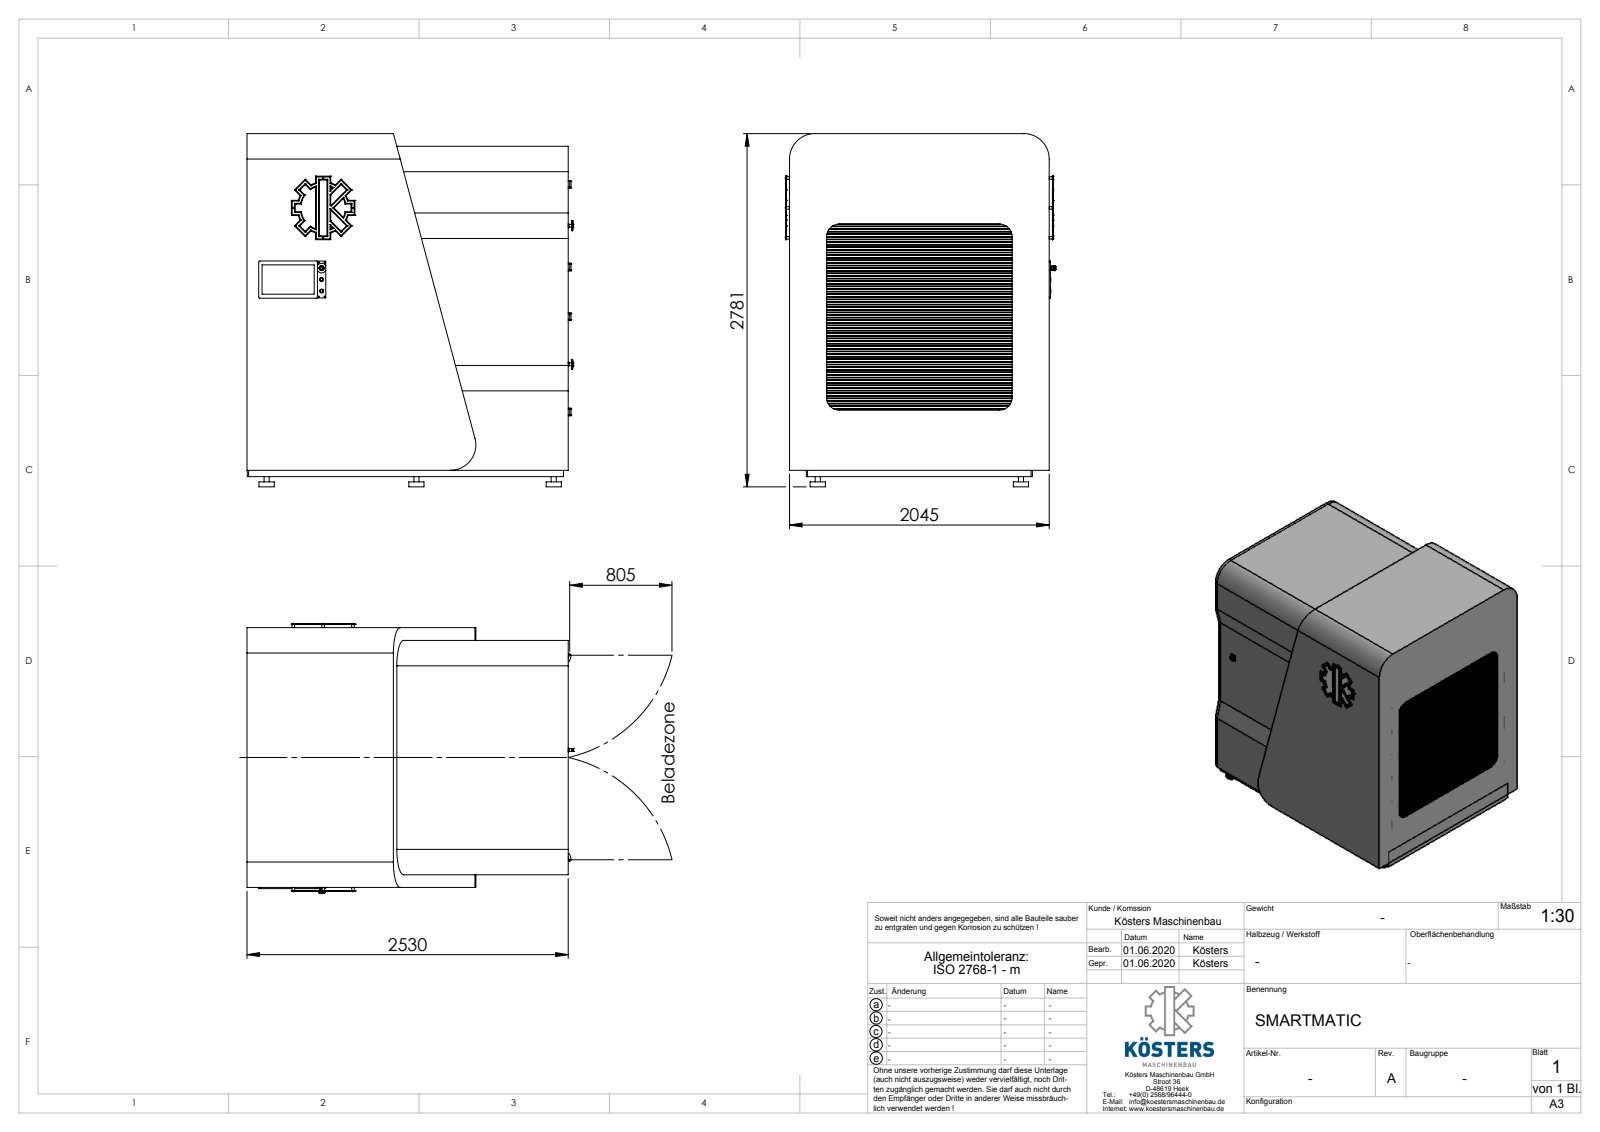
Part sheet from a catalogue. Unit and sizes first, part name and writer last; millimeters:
Units: millimetres
Overall size (bounding box): 2781 × 2568.8 × 2127.25
Round holes (diameter × count): ⌀2.5 ×148, ⌀7 ×32, ⌀4.92 ×29, ⌀2 ×6, ⌀5.1 ×6, ⌀6 ×6, ⌀4.92 ×5, ⌀5.5 ×4, ⌀26.2 ×3, ⌀1.85 ×2, ⌀2.2 ×2, ⌀5 ×2
Round bosses / shafts (diameter × count): ⌀9.5 ×8, ⌀5 ×8, ⌀20 ×7, ⌀120 ×6, ⌀40 ×6, ⌀22 ×4, ⌀27.2 ×3, ⌀21.6 ×3
Partial cylindrical surfaces — rounded edges, fillets, slot ends (radius × count): R2 ×318, R0.25 ×176, R1 ×36, R5 ×26, R1.5 ×24, R0.5 ×18, R0.3 ×16, R10 ×14
Main face-to-face distances: 2, 2043, 100, 2528, 200, 150, 1893, 2045, 98, 102
Hole centre spacings: 36, 20.5, 50.91, 1574, 1574.41, 1610, 41, 650
Volume: 985 100 000 mm³ · Surface area: 77 380 000 mm²
Bodies: 161 solids, 6215 faces (3309 planar, 2317 cylindrical, 589 other)
Part name (STEP PRODUCT): BG_Homepage_Robozell_Zusamenbau - ohne Roboter
STEP written by: SolidWorks 2013 (CONFIG_CONTROL_DESIGN)
